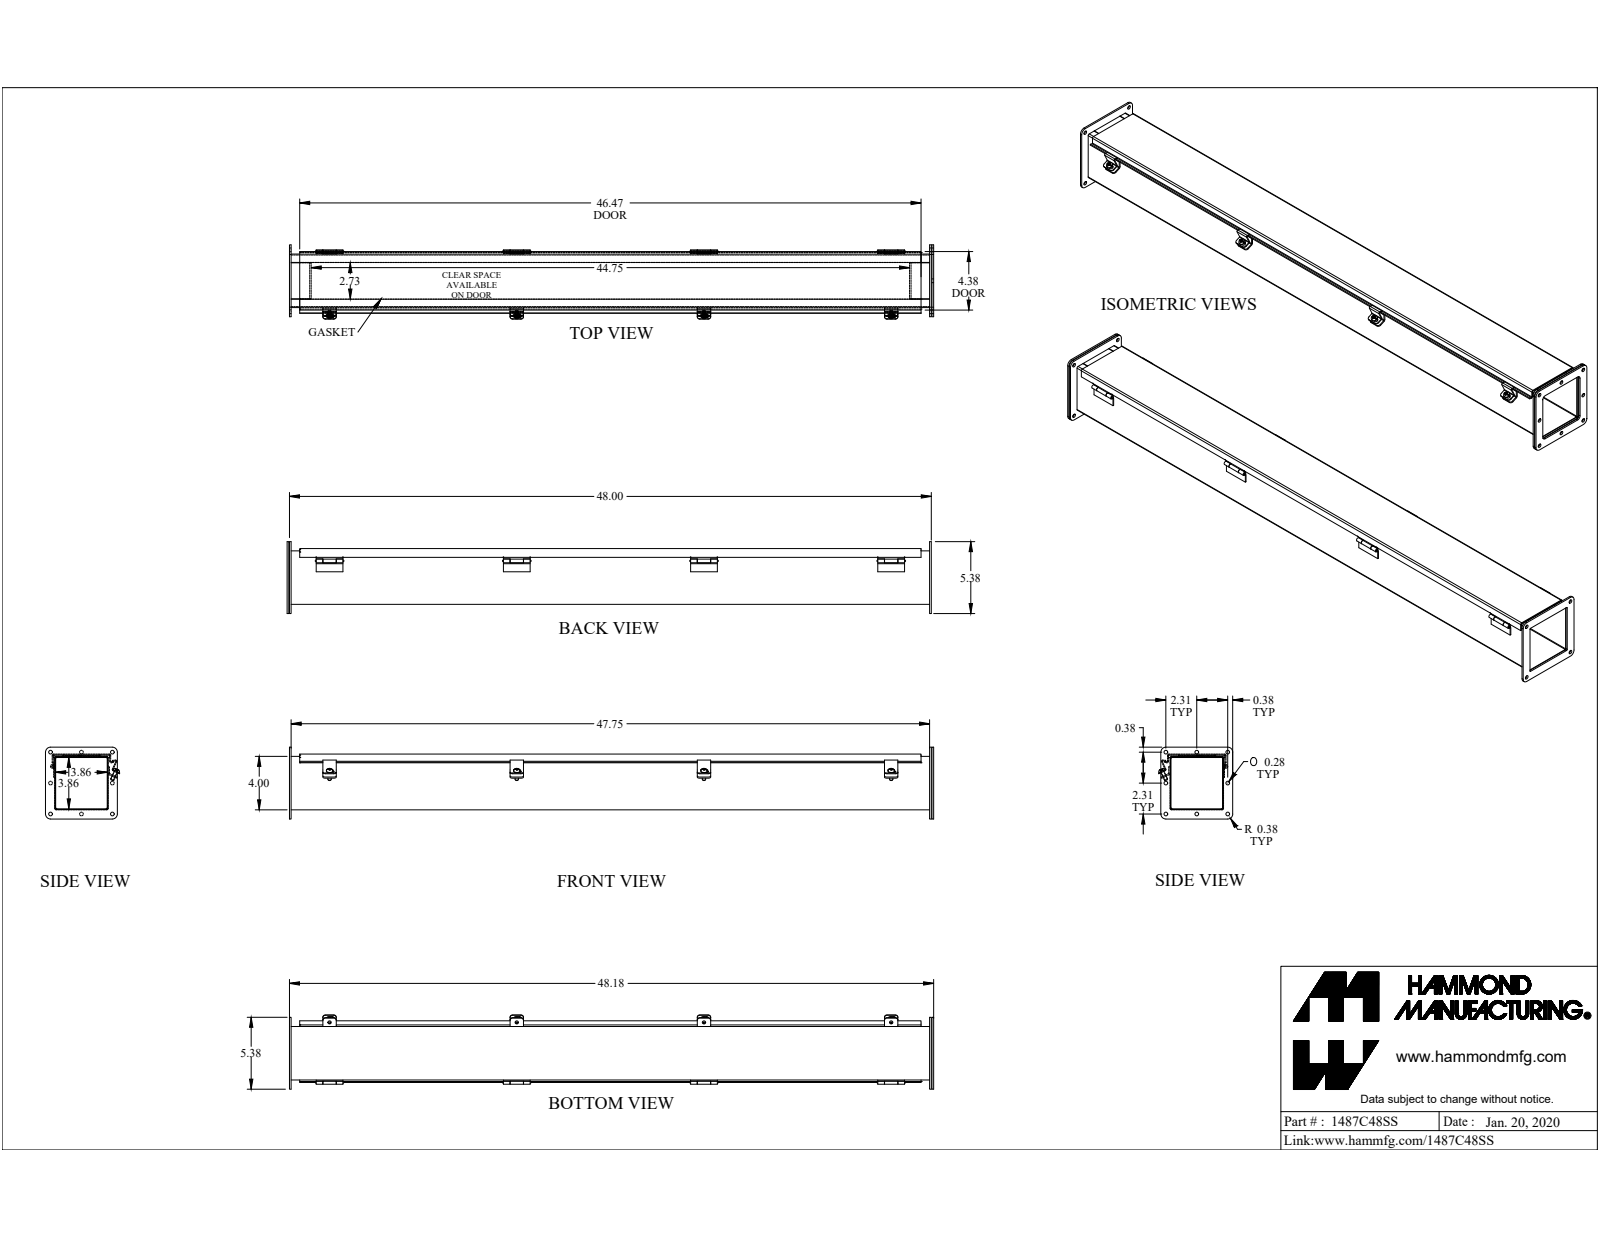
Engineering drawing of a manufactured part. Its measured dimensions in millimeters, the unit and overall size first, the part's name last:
Units: millimetres
Overall size (bounding box): 1233.1 × 141 × 136.5
Round holes (diameter × count): ⌀7.1 ×8, ⌀5.4 ×4, ⌀4.7 ×1, ⌀5 ×1, ⌀6.6 ×1, ⌀8.9 ×1
Round bosses / shafts (diameter × count): ⌀6.4 ×5, ⌀12.2 ×4, ⌀12.7 ×1, ⌀8.6 ×1, ⌀4.6 ×1
Partial cylindrical surfaces — rounded edges, fillets, slot ends (radius × count): R4.8 ×16, R0.8 ×8, R3.6 ×8, R9.5 ×8, R0.9 ×7, R2.7 ×7, R0.5 ×6, R1.6 ×4
Main face-to-face distances: 1.8, 99.8, 104.1, 101.6, 97.9, 106, 102.3, 4.7, 6.6, 4.4
Hole centre spacings: 58.8, 131.3, 117.5, 117.5, 355.6, 58.7, 83.1, 83.1
Volume: 1 398 000 mm³ · Surface area: 1 394 000 mm²
Bodies: 39 solids, 786 faces (508 planar, 208 cylindrical, 70 other)
Part name (STEP PRODUCT): 1487C48SS
STEP written by: SolidWorks 2019 (CONFIG_CONTROL_DESIGN)
